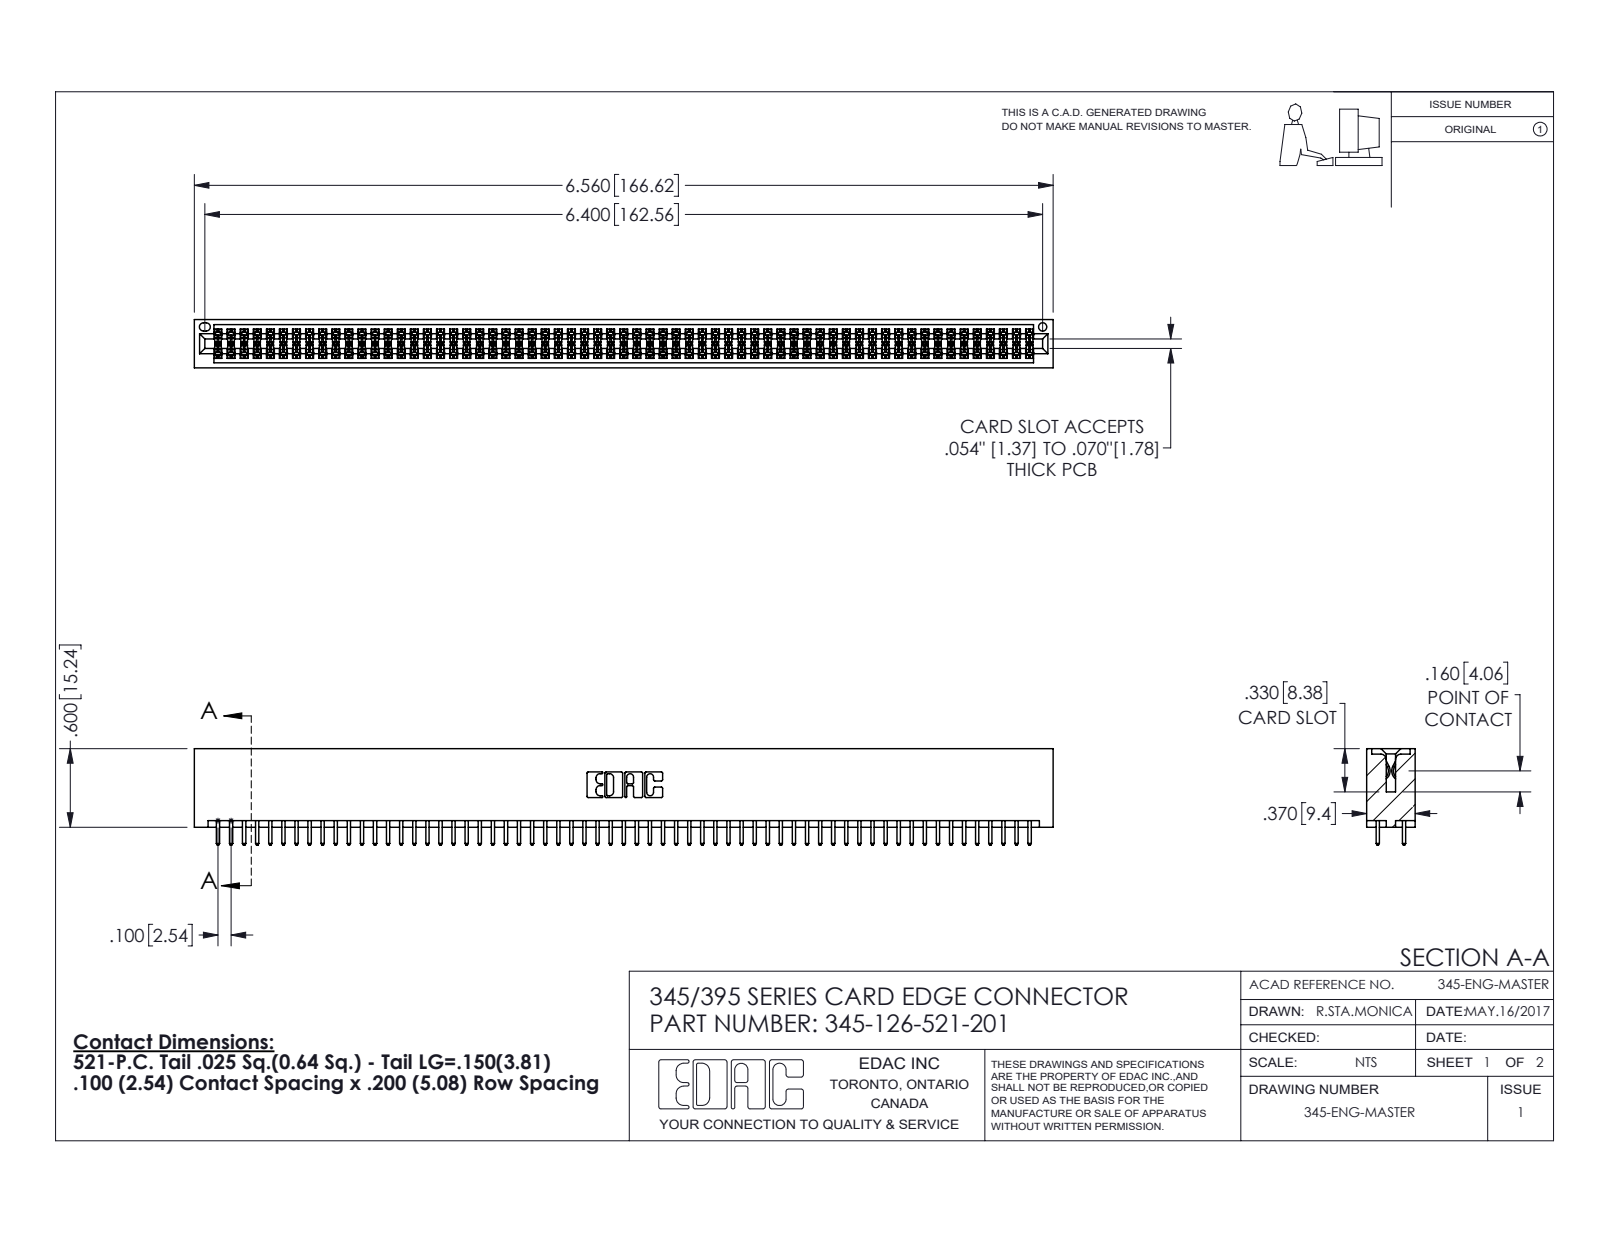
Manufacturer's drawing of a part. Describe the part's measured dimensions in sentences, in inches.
The part is named "345 Part_No Mounting Lugs; 345-126-521-201; 345-292-001_345-293-121". Its 3-D file was written by "SolidWorks 2016 (CONFIG_CONTROL_DESIGN)". It is 127 solids with 6418 faces: 4234 planar, 2184 cylindrical and 0 other. Overall it measures 6.56 by 0.737 by 0.37 inches. Its volume is 1.034 cubic inches and its surface area 39.41 square inches. Round holes: 1 of diameter 0.064. Partial cylindrical surfaces (rounded edges, fillets, slot ends): 189 of radius 0.006, 126 of radius 0.01, 22 of radius 0.01, 6 of radius 0.007, 6 of radius 0.031, 3 of radius 0.026, 2 of radius 0.014, 2 of radius 0.019. The main face-to-face distances are 0.298, 0.072, 0.2, 0.098, 0.272, 0.025, 0.37, 0.225, 0.175, 0.149.
